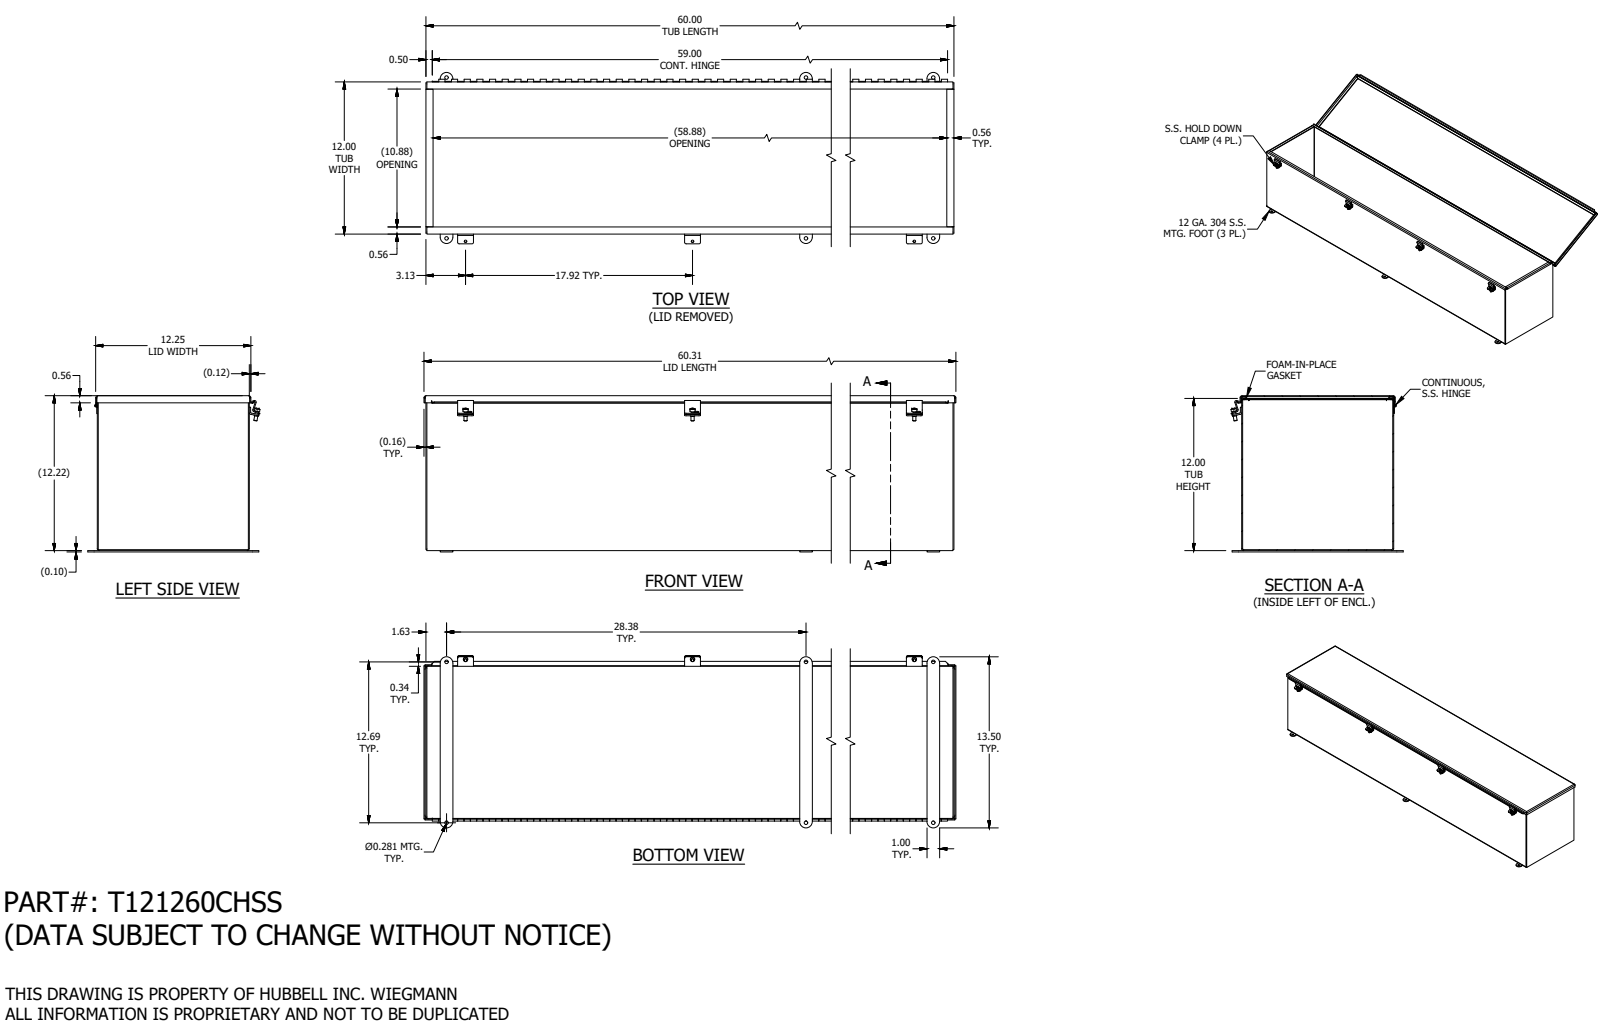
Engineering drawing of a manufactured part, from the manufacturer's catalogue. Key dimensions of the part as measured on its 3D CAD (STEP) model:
Part name (STEP PRODUCT): T121260CHSS
STEP written by: SolidWorks 2019 (AUTOMOTIVE_DESIGN)
Units: inches
Bodies: 23 solids, 1024 faces (613 planar, 365 cylindrical, 46 other)
Overall size (bounding box): 60.313 × 13.598 × 12.322
Volume: 266.4 in³ · Surface area: 7 136 in²
Round holes (diameter × count): ⌀0.11 ×8, ⌀0.281 ×6, ⌀0.196 ×4, ⌀0.116 ×1
Round bosses / shafts (diameter × count): ⌀0.41 ×4, ⌀0.344 ×4, ⌀0.25 ×4, ⌀0.2 ×1, ⌀0.1 ×1
Partial cylindrical surfaces — rounded edges, fillets, slot ends (radius × count): R0.125 ×16, R0.094 ×11, R0.168 ×11, R0.085 ×8, R0.133 ×8, R0.5 ×6, R0.242 ×4, R0.063 ×3
Main face-to-face distances: 0.074, 11.926, 12.144, 12, 11.852, 12.218, 12.07, 59.926, 59.852, 60
Hole centre spacings: 17.917, 0.75, 28.375, 31.082, 35.833, 12.687, 17.167, 17.917
